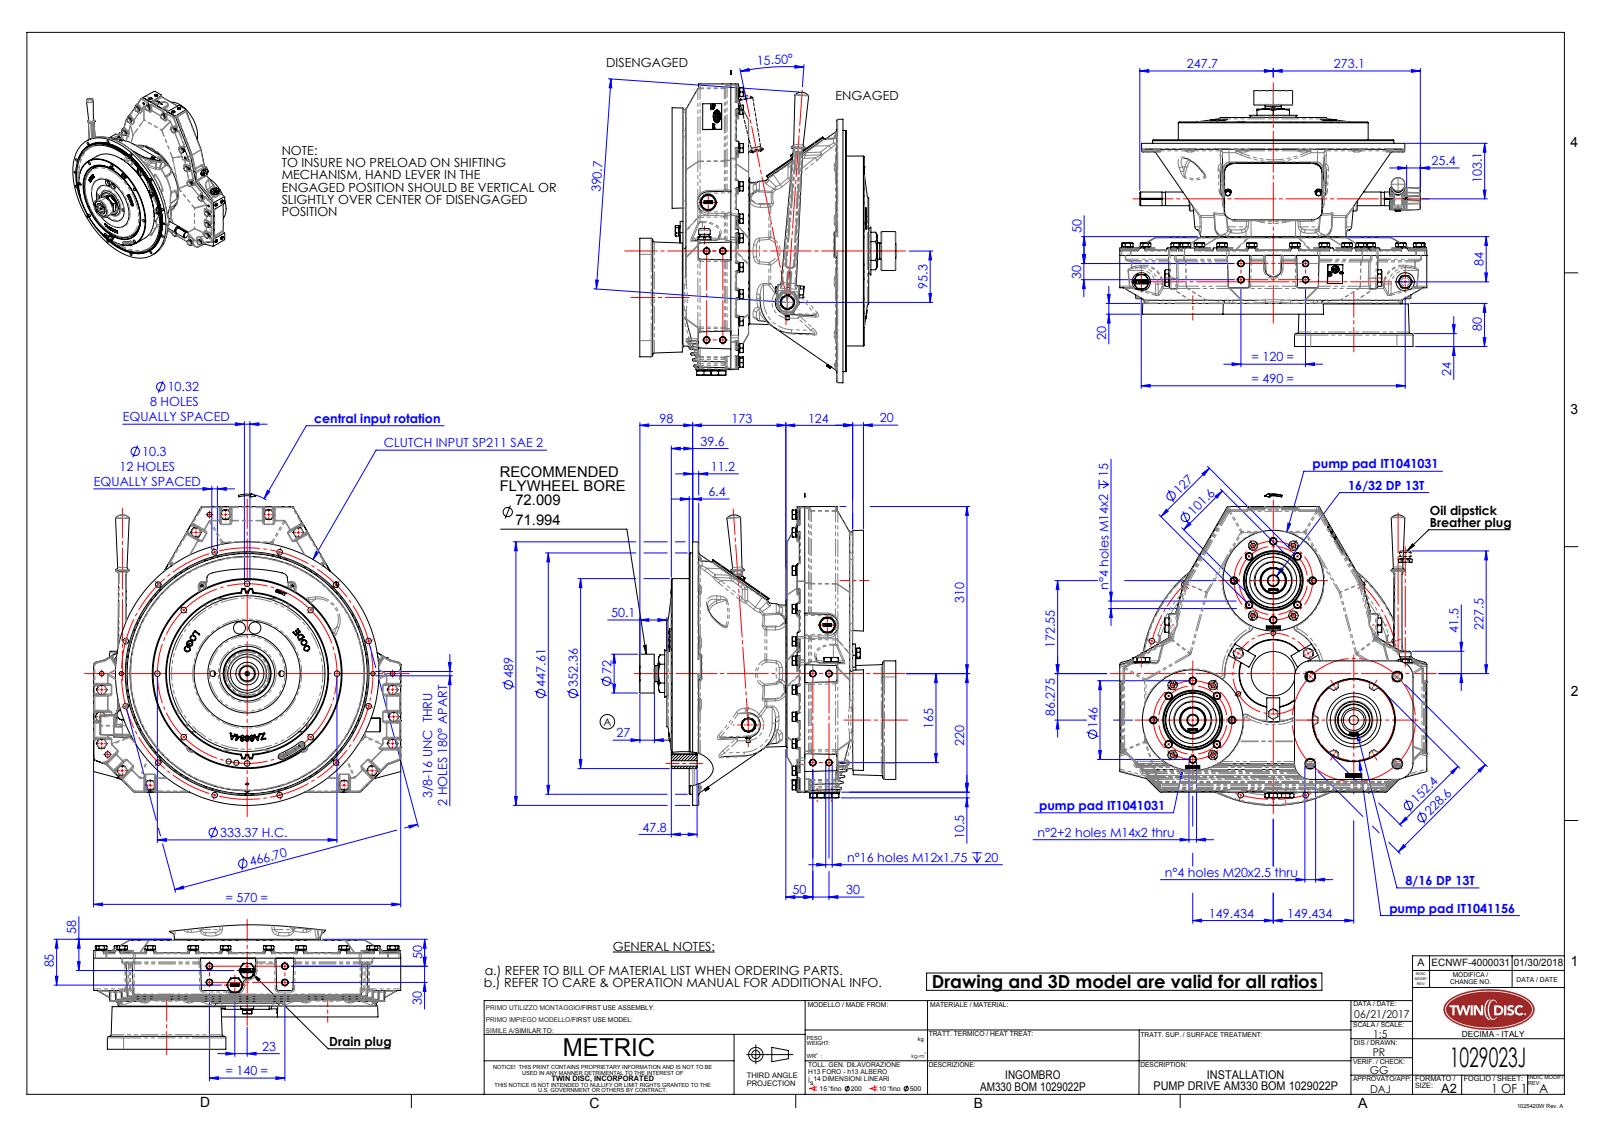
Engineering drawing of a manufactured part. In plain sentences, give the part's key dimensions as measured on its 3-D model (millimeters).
The part is named "1029023J-new; ITB00410000_rev01-installation; ITam110-013_rev01-installation; IT1041031_rev00-installation (+6 more)". Its 3-D file was written by "SolidWorks 2015 (AUTOMOTIVE_DESIGN)". It is 48 solids with 10295 faces: 3552 planar, 2692 cylindrical and 4051 other. Overall it measures 579.04 by 570 by 475.1 millimeters. Its volume is 3 713 000 cubic millimeters and its surface area 3 724 000 square millimeters. Round holes: 52 of diameter 10.2, 36 of diameter 12, 33 of diameter 8.5, 26 of diameter 10.5, 16 of diameter 11, 12 of diameter 10.3, 9 of diameter 10, 9 of diameter 17, 8 of diameter 10.32, 8 of diameter 30, 7 of diameter 13, 5 of diameter 6. Round bosses or shafts: 42 of diameter 10, 34 of diameter 18.1, 34 of diameter 16.2, 18 of diameter 14, 8 of diameter 16, 5 of diameter 20, 4 of diameter 125, 4 of diameter 87.07. Partial cylindrical surfaces (rounded edges, fillets, slot ends): 352 of radius 2, 224 of radius 0.1, 157 of radius 3, 92 of radius 0.25, 80 of radius 5, 51 of radius 6.5, 48 of radius 1.52, 46 of radius 0.25. The main face-to-face distances are 89, 11.5, 33, 21.5, 110.5, 122, 144, 85.5, 83.5, 118.5. The hole center spacings are 120, 57.4, 75, 138.58, 30, 207.84, 282.91, 10.
